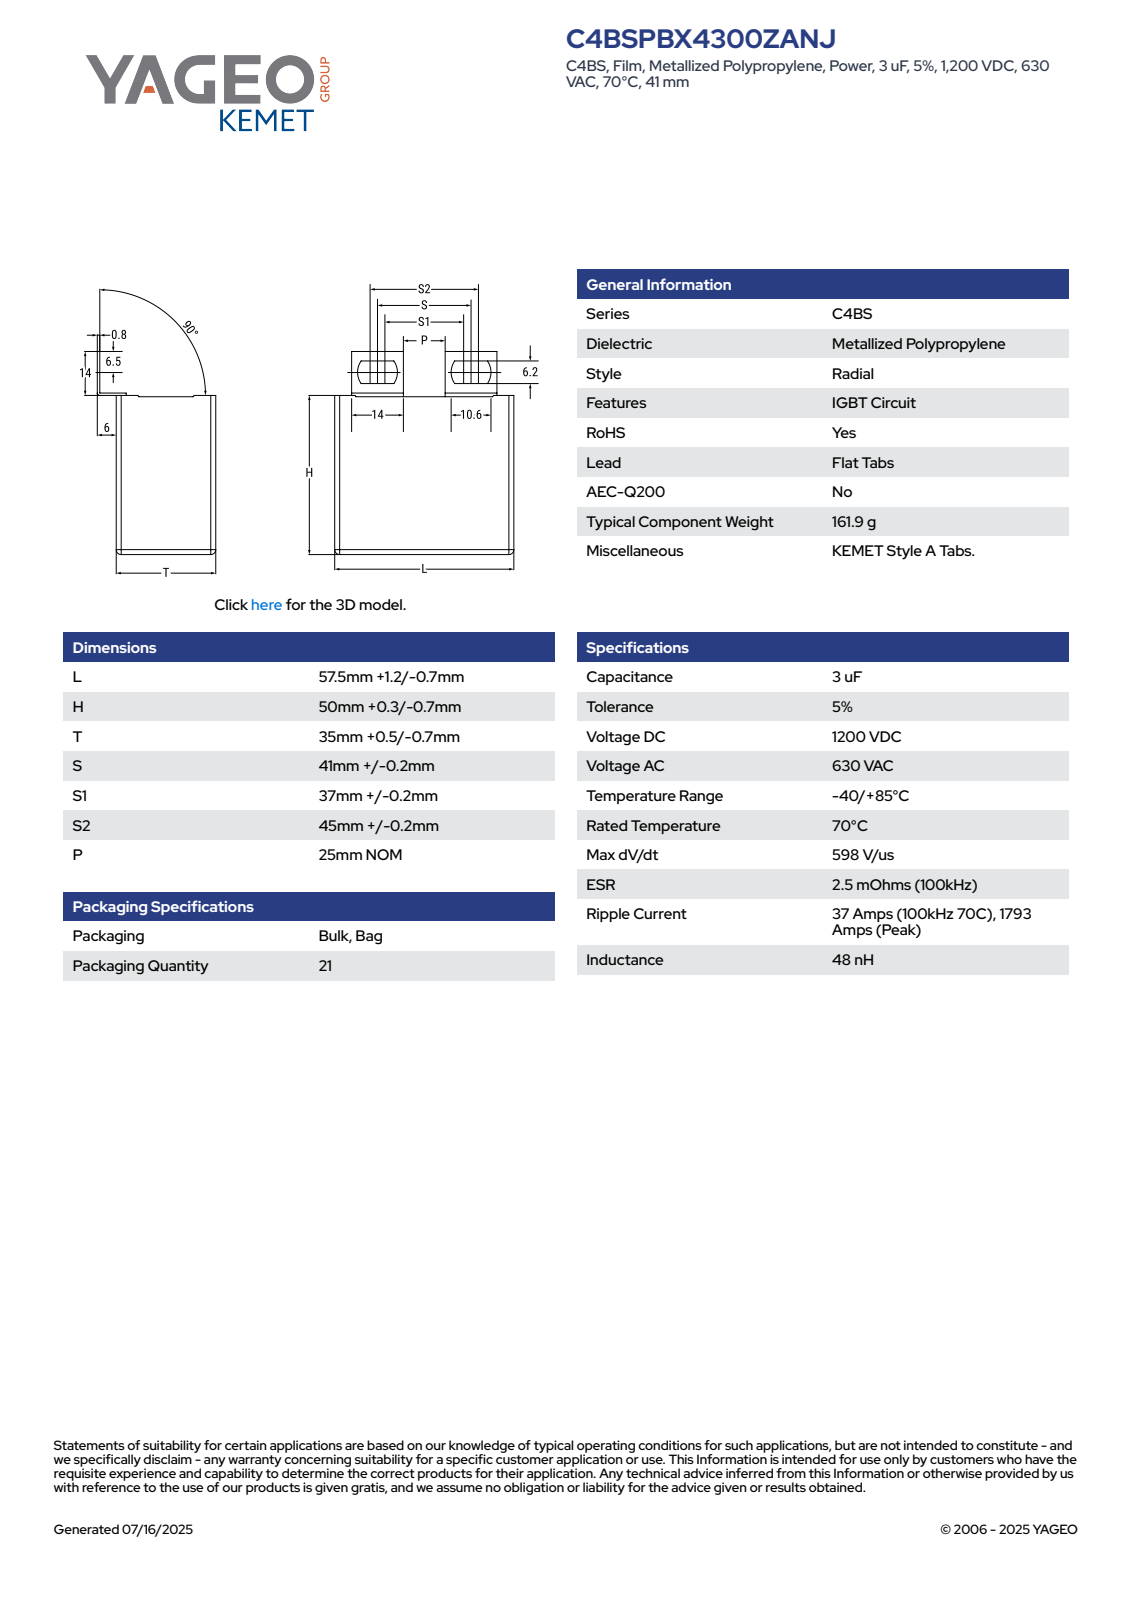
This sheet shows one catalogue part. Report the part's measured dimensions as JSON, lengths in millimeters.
{"part_name": "CFP_C4BA_57.5X50X35_L58.7H50.3T35.5S41.2", "step_written_by": "SolidWorks 2014 (AUTOMOTIVE_DESIGN)", "units": "millimeters", "bodies": {"solids": 4, "faces": 97, "planar": 91, "cylindrical": 6, "other": 0}, "overall_size": [64.9, 58.7, 41.51], "volume_mm3": 105156, "surface_area_mm2": 15569, "partial_cylinders_radius": [[6.1, 4]], "face_to_face_distances": [35.5, 50.25, 58.7, 0.6, 50.3, 50.9, 0.65, 41.5, 6, 40.9]}
